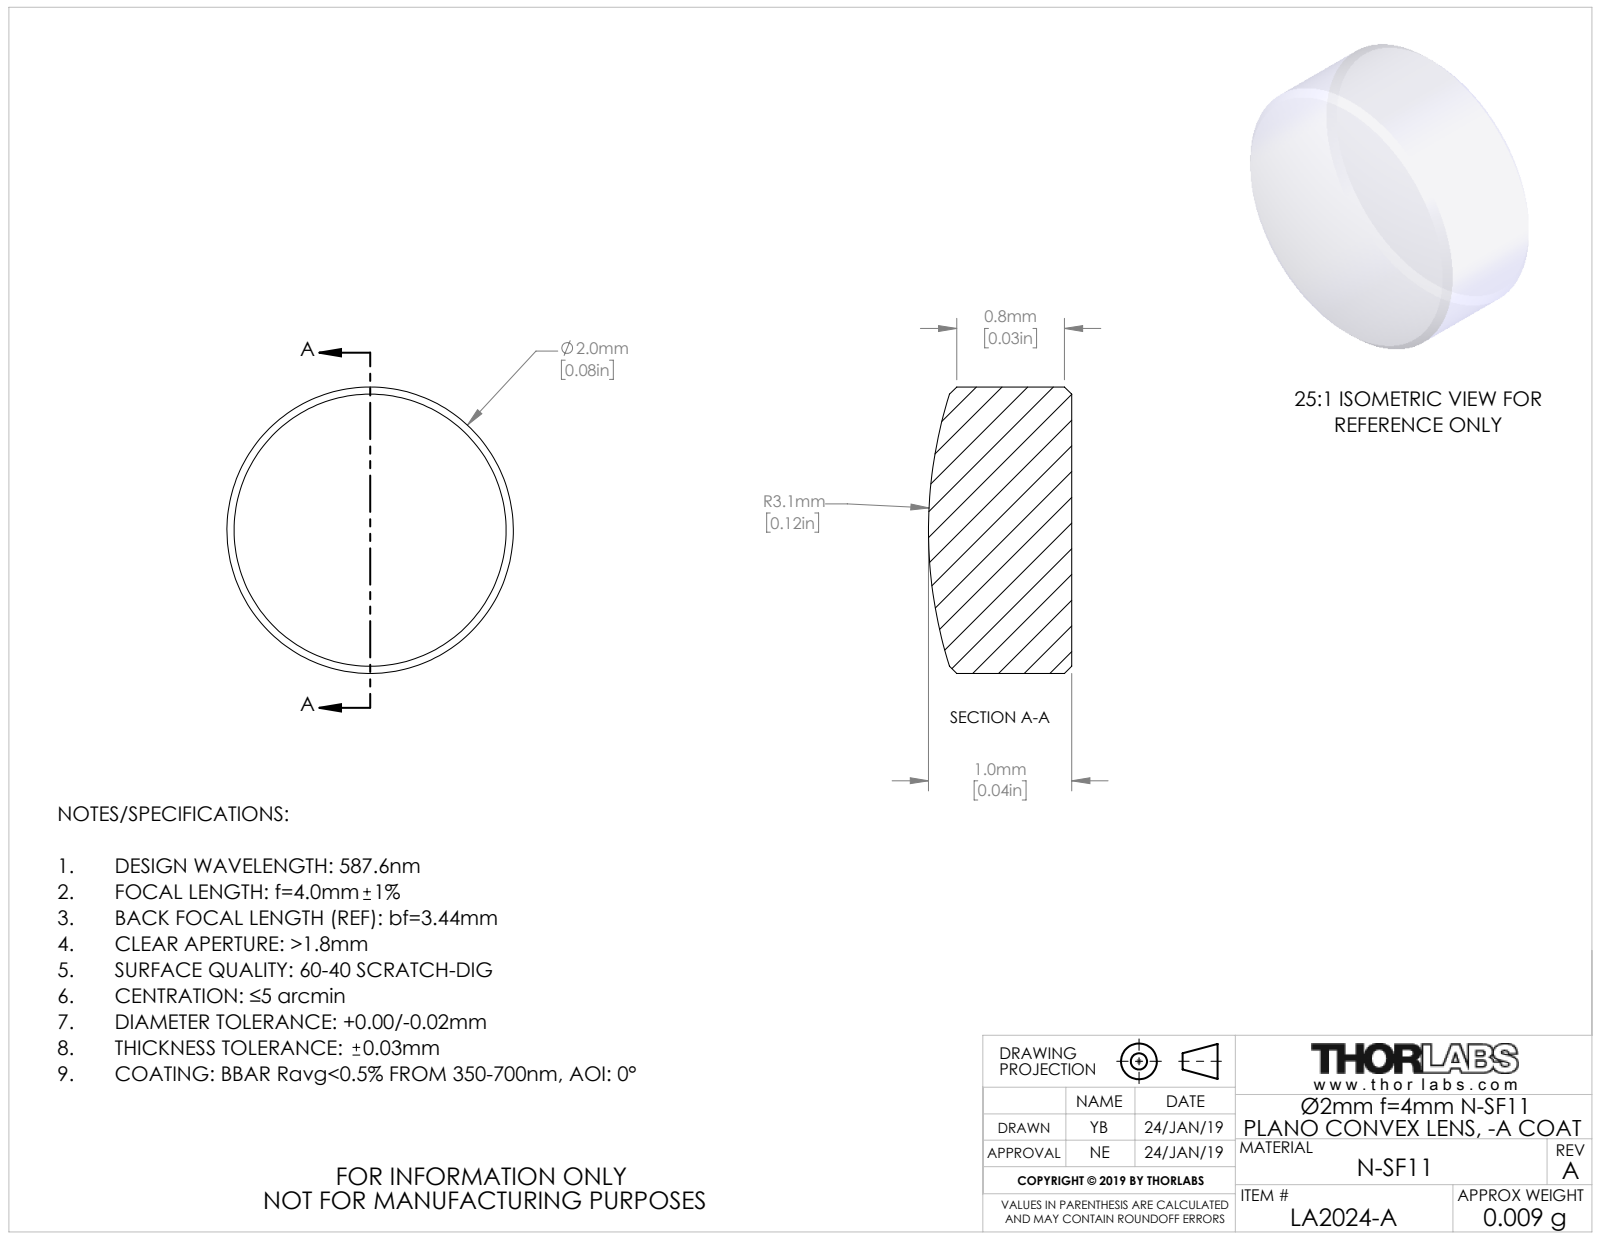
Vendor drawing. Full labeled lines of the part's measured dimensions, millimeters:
Part name (STEP PRODUCT): TTN162747-E0W
STEP written by: SolidWorks 2018 (CONFIG_CONTROL_DESIGN)
Units: millimetres
Bodies: 1 solid, 9 faces (1 planar, 2 cylindrical, 6 other)
Overall size (bounding box): 2 × 2 × 1
Volume: 3 mm³ · Surface area: 11 mm²
Round bosses / shafts (diameter × count): ⌀2 ×1
